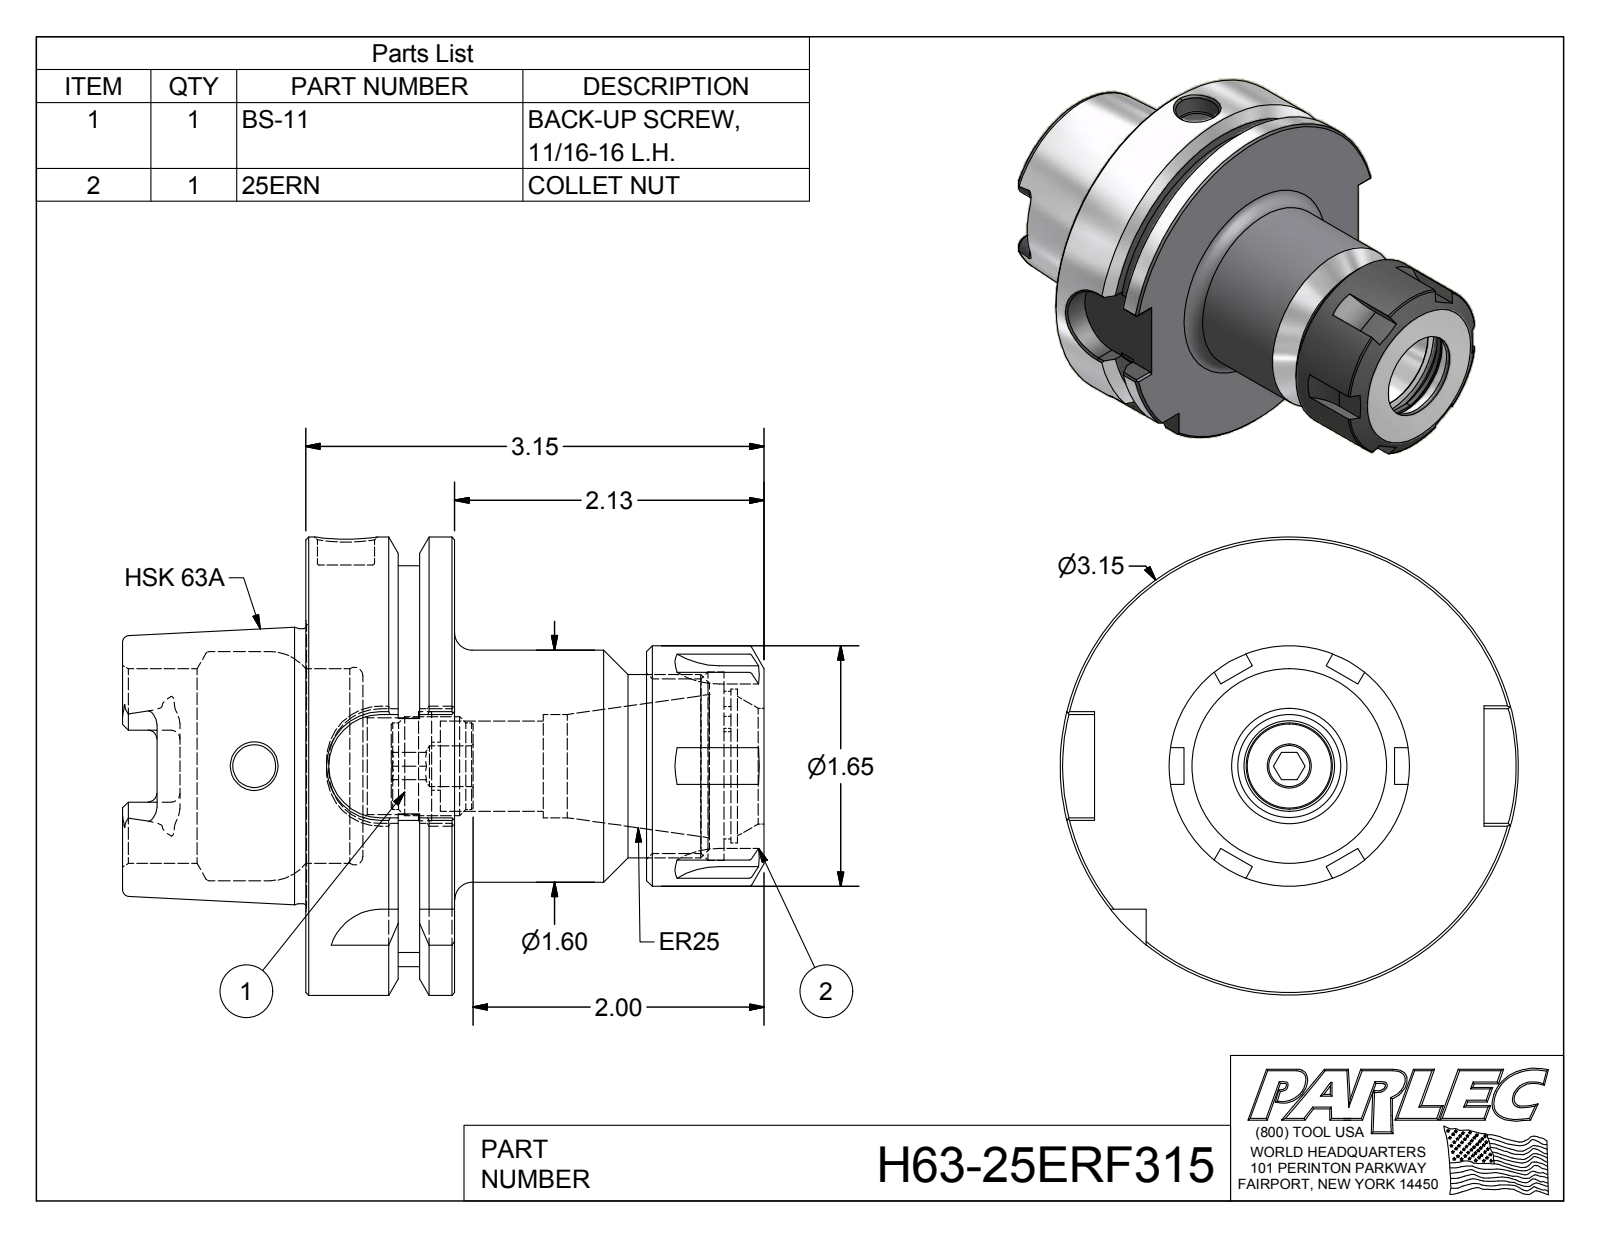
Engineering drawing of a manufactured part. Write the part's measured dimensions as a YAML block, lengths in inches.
part_name: "H63-25ERF315; H63-25ER3-1; BS-11; 25ERN"
step_written_by: "Autodesk Inventor 2012 (AUTOMOTIVE_DESIGN)"
units: inches
bodies: {solids: 3, faces: 213, planar: 91, cylindrical: 55, other: 67}
overall_size: [4.41, 3.15, 3.15]
volume: 10.96
surface_area: 67.45
round_holes:
  - {diameter: 0.28, count: 1}
  - {diameter: 0.295, count: 1}
  - {diameter: 0.331, count: 1}
  - {diameter: 0.394, count: 1}
  - {diameter: 0.62, count: 1}
  - {diameter: 0.666, count: 1}
  - {diameter: 0.71, count: 1}
  - {diameter: 0.749, count: 1}
  - {diameter: 0.794, count: 1}
  - {diameter: 1.057, count: 1}
  - {diameter: 1.201, count: 1}
  - {diameter: 1.294, count: 1}
round_bosses_or_shafts:
  - {diameter: 3.15, count: 1}
  - {diameter: 1.891, count: 1}
  - {diameter: 1.654, count: 1}
  - {diameter: 1.595, count: 1}
  - {diameter: 1.26, count: 1}
  - {diameter: 0.681, count: 1}
  - {diameter: 0.595, count: 1}
partial_cylinders:
  - {radius: 0.059, count: 6}
  - {radius: 0.5, count: 6}
  - {radius: 0.113, count: 4}
  - {radius: 0.354, count: 4}
  - {radius: 0.472, count: 1}
  - {radius: 0.515, count: 1}
  - {radius: 1.378, count: 1}
face_to_face_distances: [1.024, 0.241, 0.389, 3.15, 2.126, 0.394, 0.63, 2.756, 0.783, 2.367]
